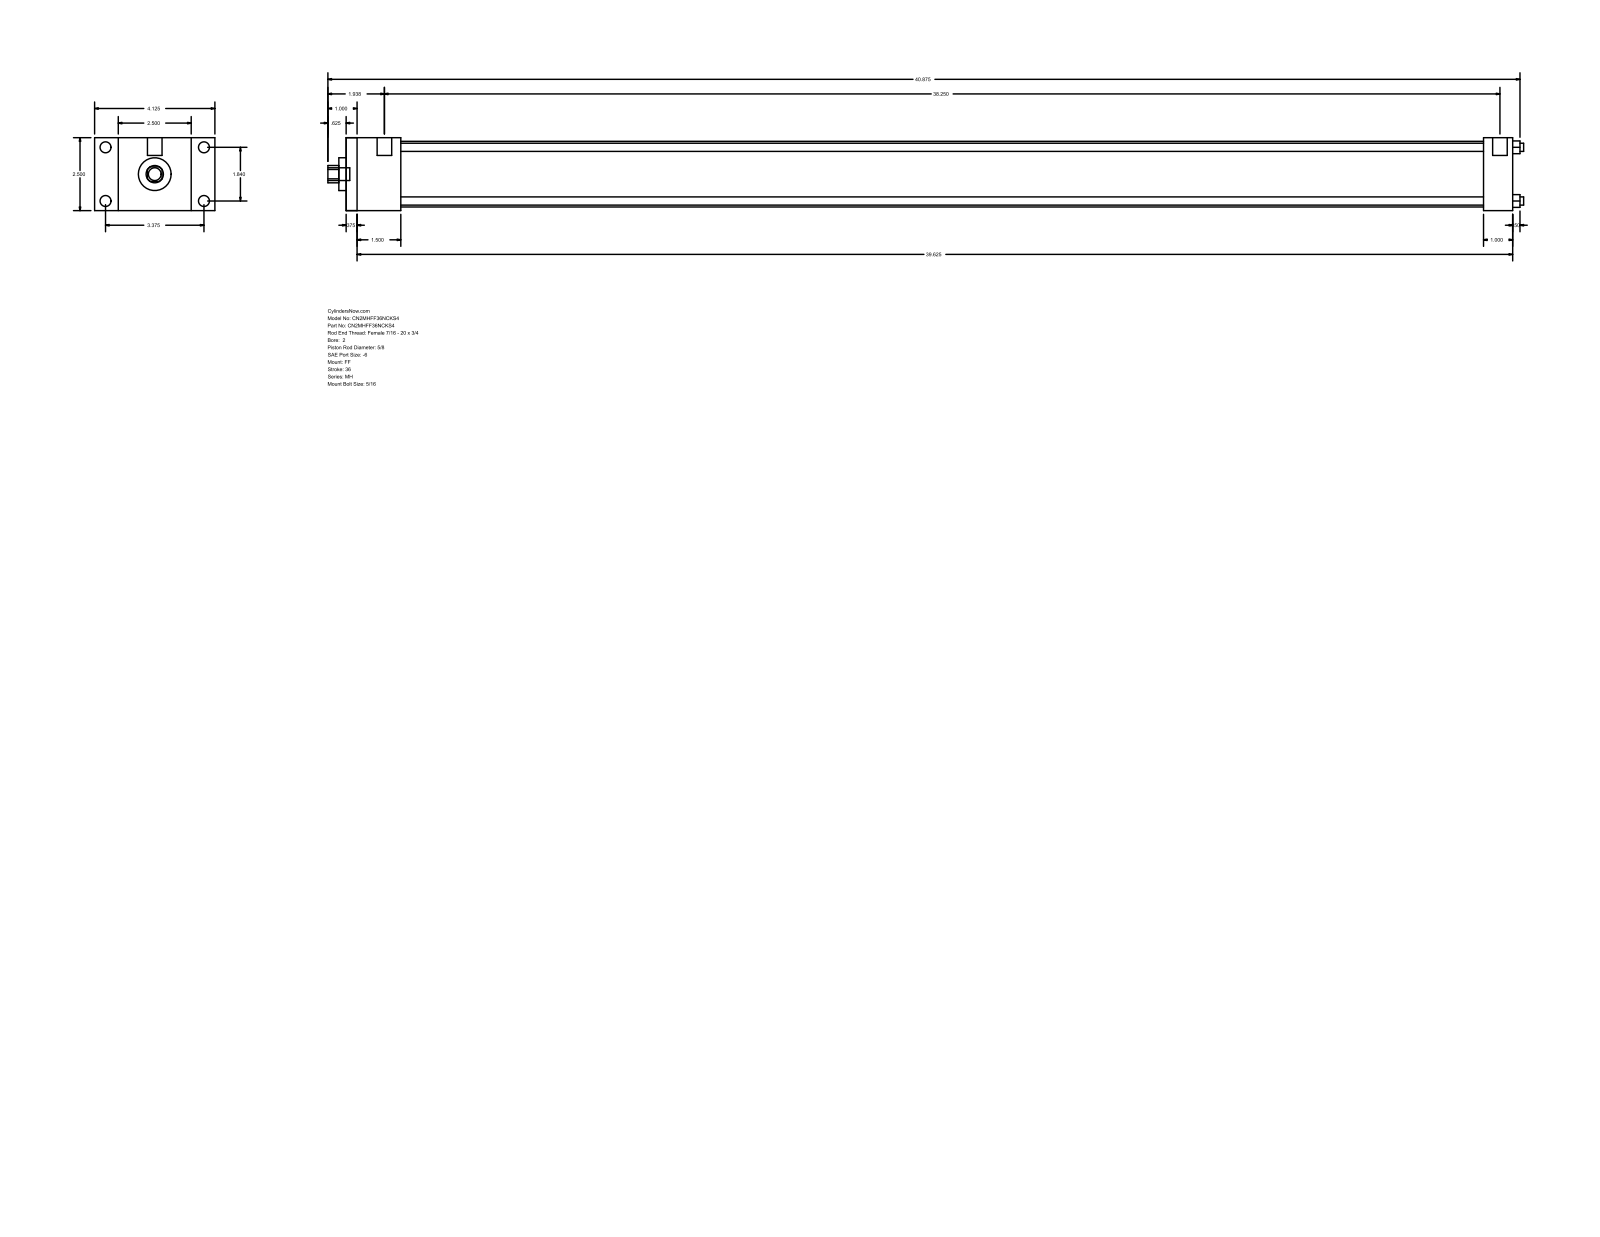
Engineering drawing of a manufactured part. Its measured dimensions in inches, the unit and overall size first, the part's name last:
Units: inches
Overall size (bounding box): 41 × 4.125 × 2.5
Round holes (diameter × count): ⌀0.281 ×4, ⌀0.625 ×1, ⌀1.125 ×1, ⌀2.25 ×1
Round bosses / shafts (diameter × count): ⌀0.375 ×4, ⌀0.219 ×4, ⌀0.5 ×2, ⌀0.437 ×1
Partial cylindrical surfaces — rounded edges, fillets, slot ends (radius × count): R0.297 ×1
Main face-to-face distances: 2.5, 40, 0.375, 39.625, 1, 1.5, 1.875, 39, 38.625, 37.125
Hole centre spacings: 1.301, 1.84, 2.602
Bodies: 0 solids, 92 faces (64 planar, 28 cylindrical, 0 other)
Part name (STEP PRODUCT): MH_FF__0200_0.625
STEP written by: GSSL Pune (CONFIG_CONTROL_DESIGN)
